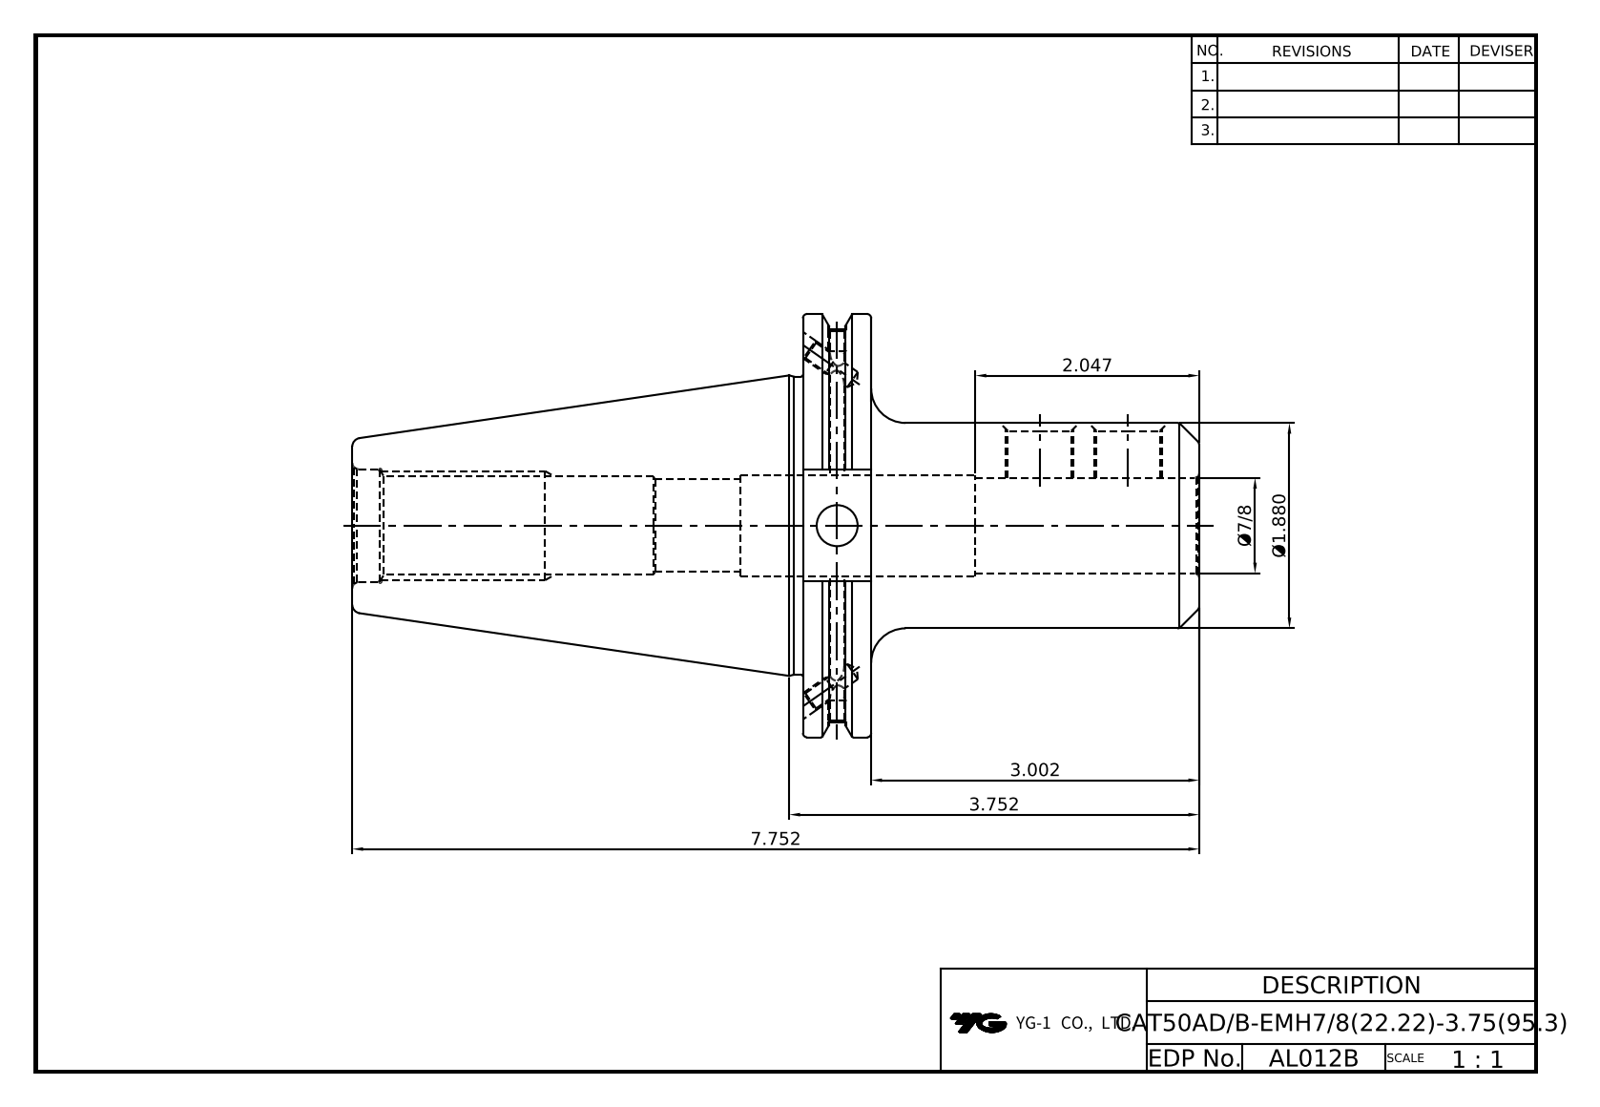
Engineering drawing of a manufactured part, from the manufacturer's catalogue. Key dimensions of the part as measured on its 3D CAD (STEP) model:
Part name (STEP PRODUCT): LO-CAT50ADB-EMH22.225-95.3
STEP written by: Autodesk Inventor 2022 (AUTOMOTIVE_DESIGN)
Units: millimetres
Bodies: 1 solid, 91 faces (39 planar, 28 cylindrical, 24 other)
Overall size (bounding box): 196.9 × 98.42 × 94.69
Volume: 418 994 mm³ · Surface area: 61 341 mm²
Round holes (diameter × count): ⌀3.24 ×2, ⌀4.13 ×2, ⌀4.2 ×2, ⌀5 ×2, ⌀14.35 ×2, ⌀9.53 ×1, ⌀21.5 ×1, ⌀21.97 ×1, ⌀22.23 ×1, ⌀23.43 ×1, ⌀26.2 ×1
Round bosses / shafts (diameter × count): ⌀98.42 ×1, ⌀91.29 ×1, ⌀69.25 ×1, ⌀47.75 ×1
Main face-to-face distances: 15.88, 92.13, 76.25, 104.77, 120.65, 196.9, 73.03, 25.9, 110.82, 6.05
Hole centre spacings: 20.6
